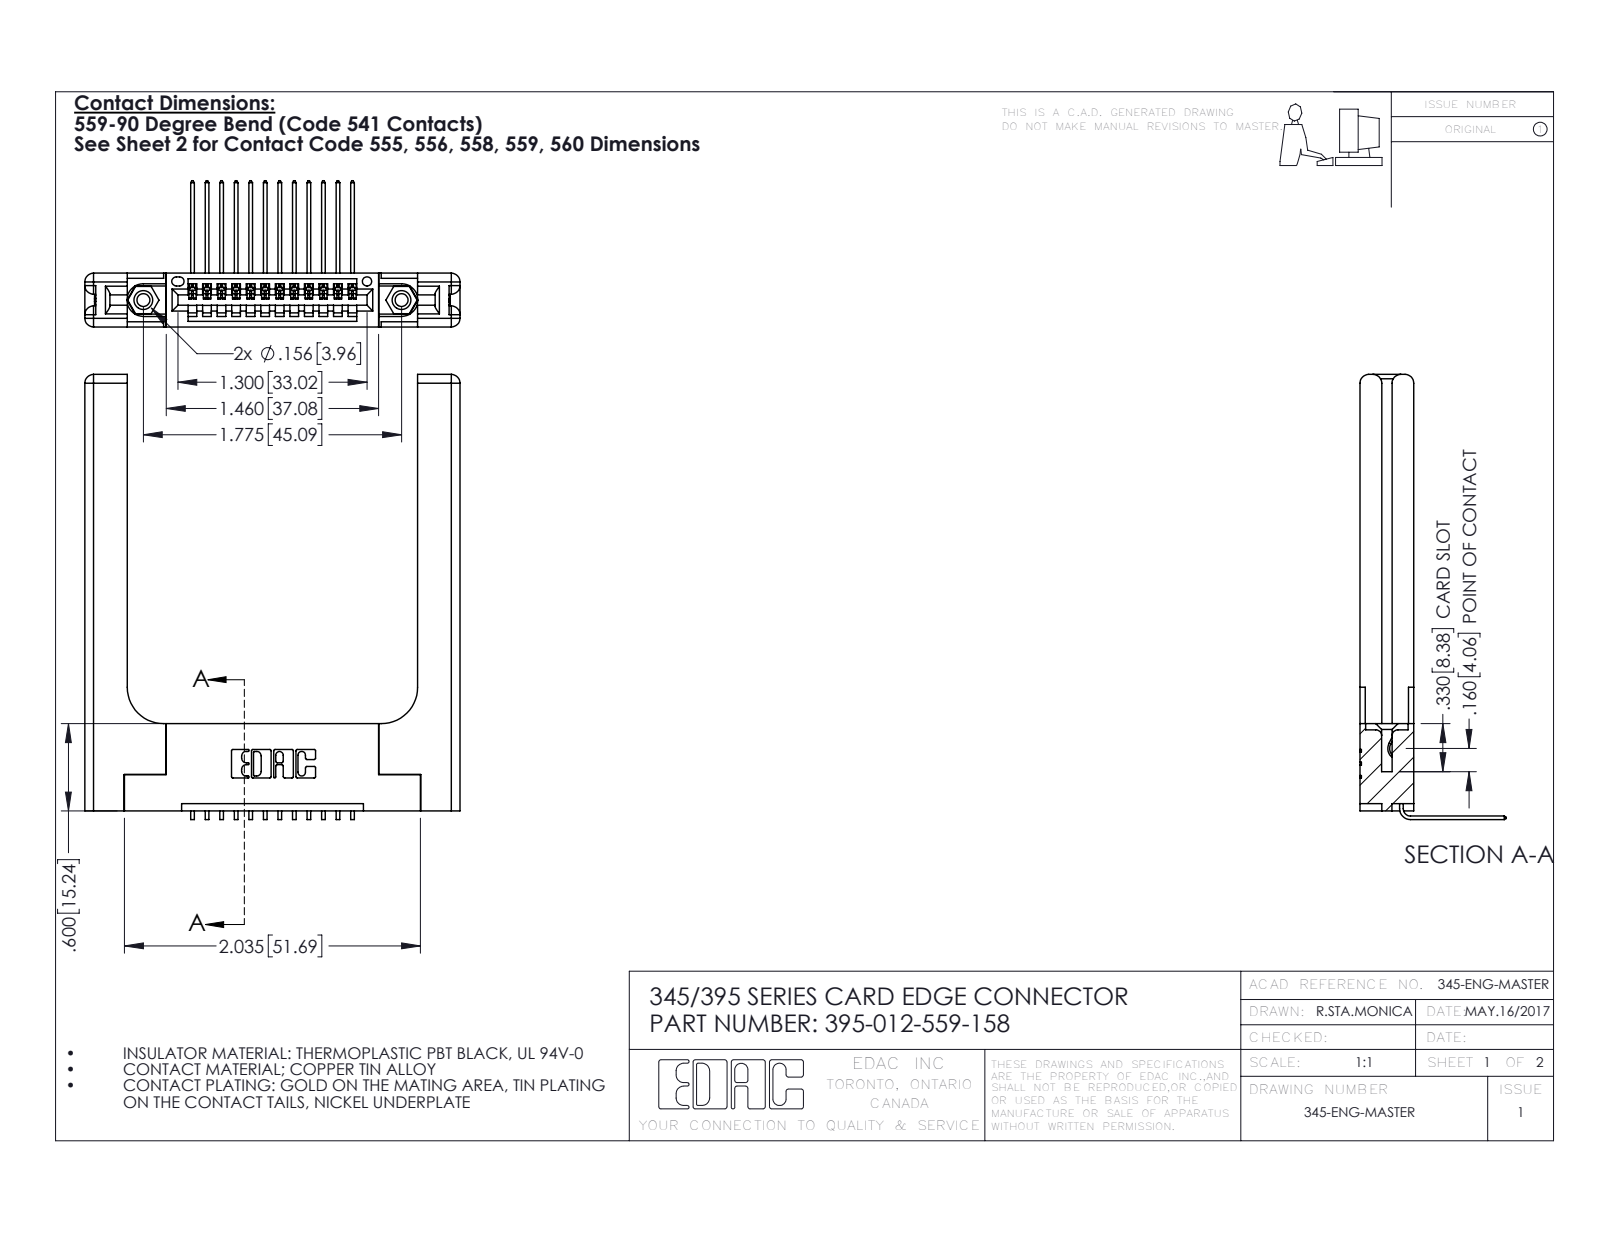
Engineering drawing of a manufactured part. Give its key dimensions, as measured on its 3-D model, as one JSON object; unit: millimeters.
{"part_name": "345-250-001_345-250-001-102; 395-012-559-158; 345-292-001_558 559 Tail - 1; 345 Part_Flush Mounting Lugs - 0.156 Dia-TH (+1 more)", "step_written_by": "SolidWorks 2016 (CONFIG_CONTROL_DESIGN)", "units": "millimeters", "bodies": {"solids": 17, "faces": 1102, "planar": 732, "cylindrical": 310, "other": 60}, "overall_size": [77.7, 65.5, 25.5], "volume_mm3": 14500, "surface_area_mm2": 13130, "round_holes": [[2.3, 2], [3.2, 2], [4, 2], [1.6, 1]], "round_bosses_or_shafts": [[3.9, 2]], "partial_cylinders_radius": [[0.2, 24], [0.3, 22], [1.5, 16], [0.2, 6], [0.8, 6], [0.7, 3], [0.8, 2], [0.8, 2]], "face_to_face_distances": [9.4, 1.8, 3.8, 5.6, 2, 3.8, 7.6, 5.1, 50.7, 1.8], "hole_center_spacings": [6.9, 39.2, 45.1]}
